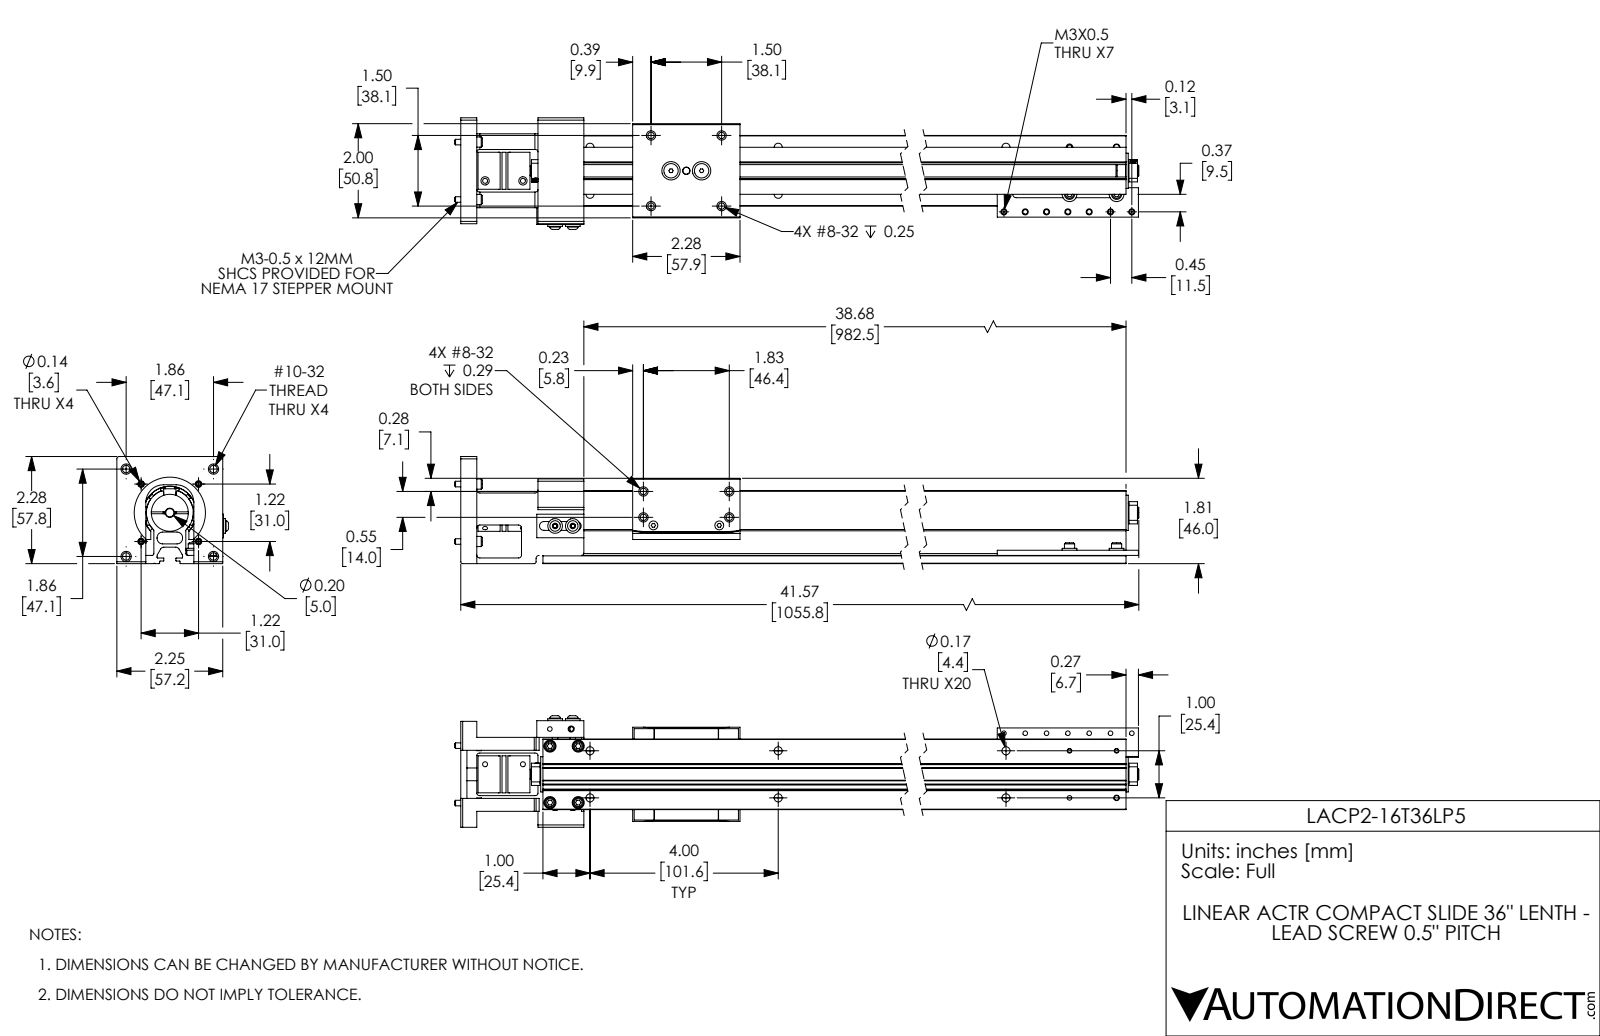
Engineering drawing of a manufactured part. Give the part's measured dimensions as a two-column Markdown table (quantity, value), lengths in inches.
| quantity | value |
| --- | --- |
| part name | LACP2-16T36LP5; LACP2-16T36LP5_BLOCK; LACP2-16T36LP5_BODY |
| STEP written by | SolidWorks 2017 (AUTOMOTIVE_DESIGN) |
| units | inches |
| bodies | 46 solids, 1264 faces (502 planar, 493 cylindrical, 269 other) |
| overall size | 41.7 × 2.37 × 2.275 |
| volume | 37.32 in³ |
| surface area | 566.1 in² |
| round holes (diameter × count) | 0.172 × 20, 0.098 × 18, 0.136 × 10, 0.141 × 4, 0.147 × 4, 0.159 × 4, 0.257 × 4, 0.099 × 2, 0.106 × 2, 0.118 × 2, 0.125 × 2, 0.125 × 2 |
| round bosses / shafts (diameter × count) | 0.217 × 10, 0.118 × 10, 0.312 × 4, 0.118 × 3, 0.307 × 2, 0.224 × 2, 0.164 × 2, 0.138 × 2 |
| partial cylindrical surfaces (radius × count) | 0.01 × 17, 0.05 × 9, 0.039 × 8, 0.065 × 7, 0.02 × 4, 0.074 × 4, 0.079 × 4, 0.118 × 4 |
| main face-to-face distances | 0.175, 0.679, 0.411, 1.089, 0.67, 0.495, 0.419, 0.244, 0.251, 0.175 |
| hole center spacings | 1, 4, 4.123, 16, 16.031, 8, 8, 8.062 |
